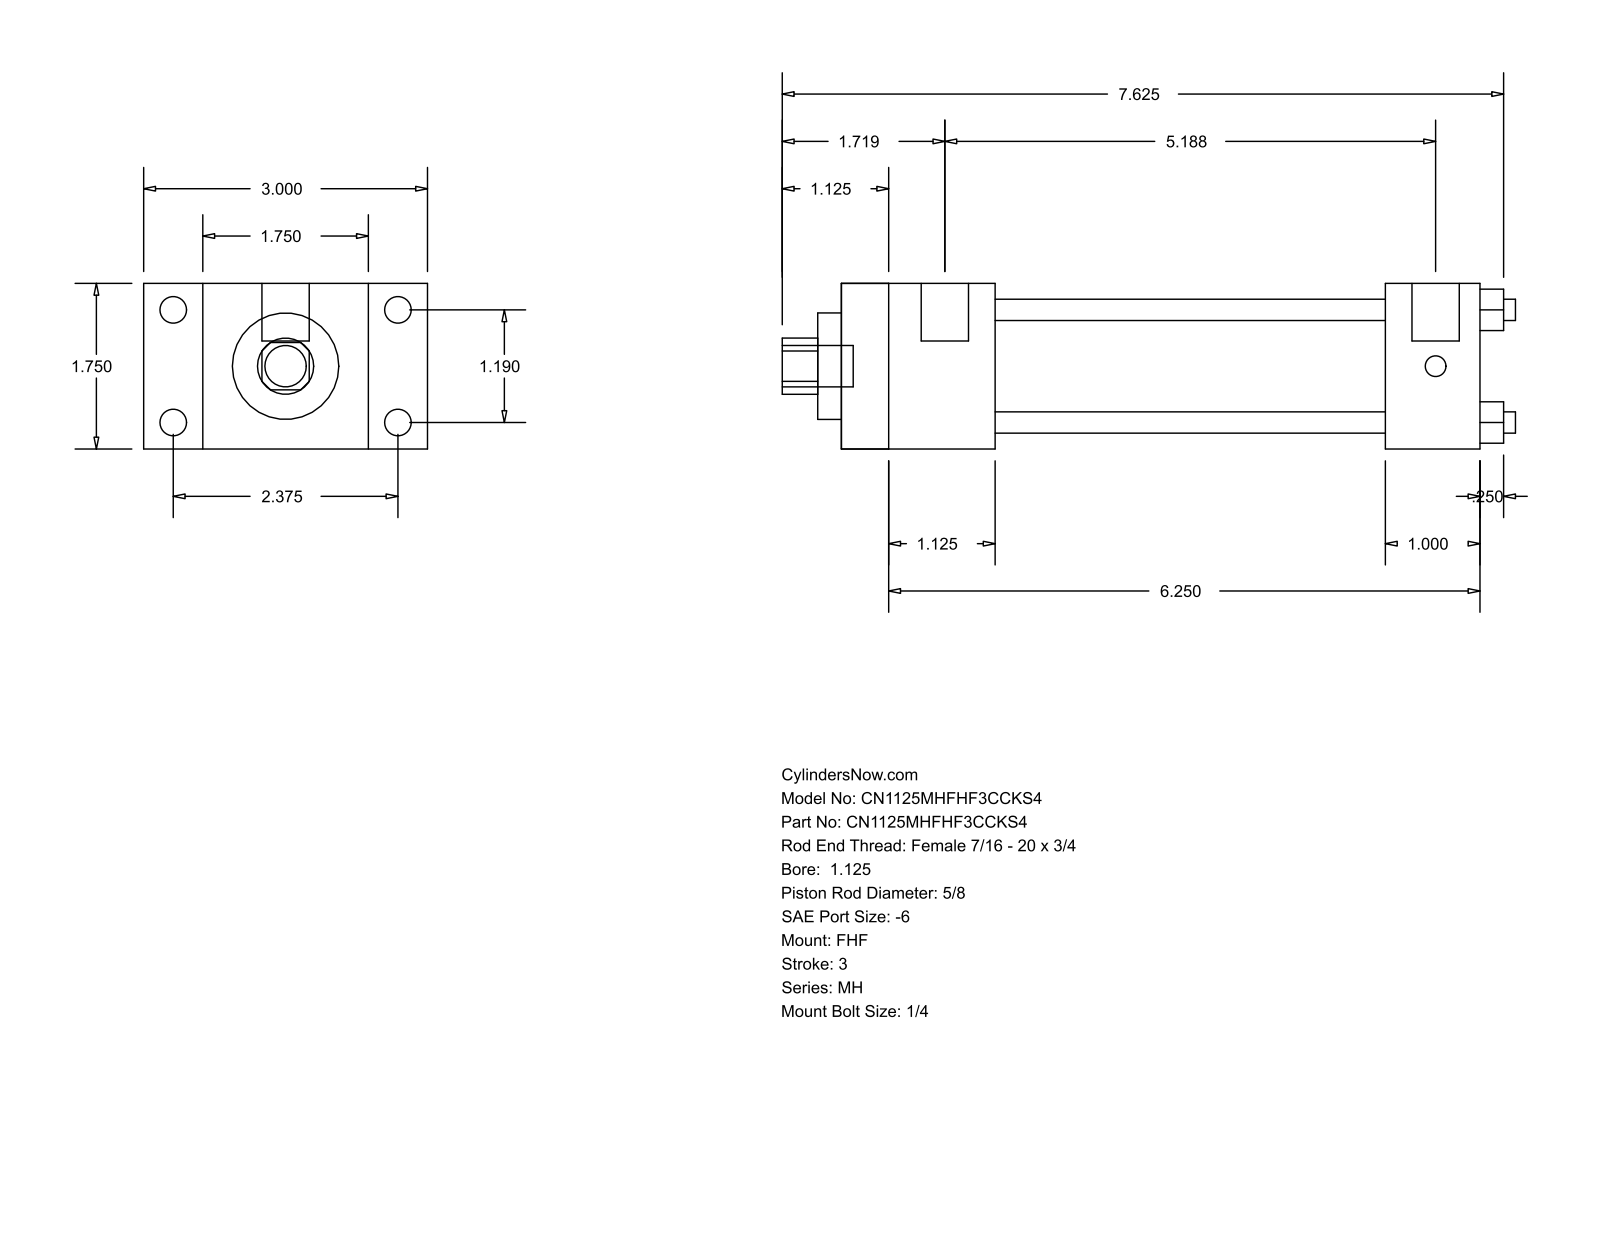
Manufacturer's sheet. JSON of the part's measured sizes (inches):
{"part_name": "MH_FHF__0112_0.625", "step_written_by": "GSSL Pune (CONFIG_CONTROL_DESIGN)", "units": "inches", "bodies": {"solids": 0, "faces": 88, "planar": 60, "cylindrical": 28, "other": 0}, "overall_size": [7.75, 3, 1.75], "round_holes": [[0.225, 4], [0.625, 1], [1.125, 1], [1.375, 1]], "round_bosses_or_shafts": [[0.281, 4], [0.219, 4], [0.5, 2], [0.437, 1]], "partial_cylinders_radius": [[0.297, 1]], "face_to_face_distances": [1.75, 0.625, 2.375, 1.625, 3, 6.75, 5.125, 5.75, 4.125, 1], "hole_center_spacings": [0.841, 1.19, 1.683]}
